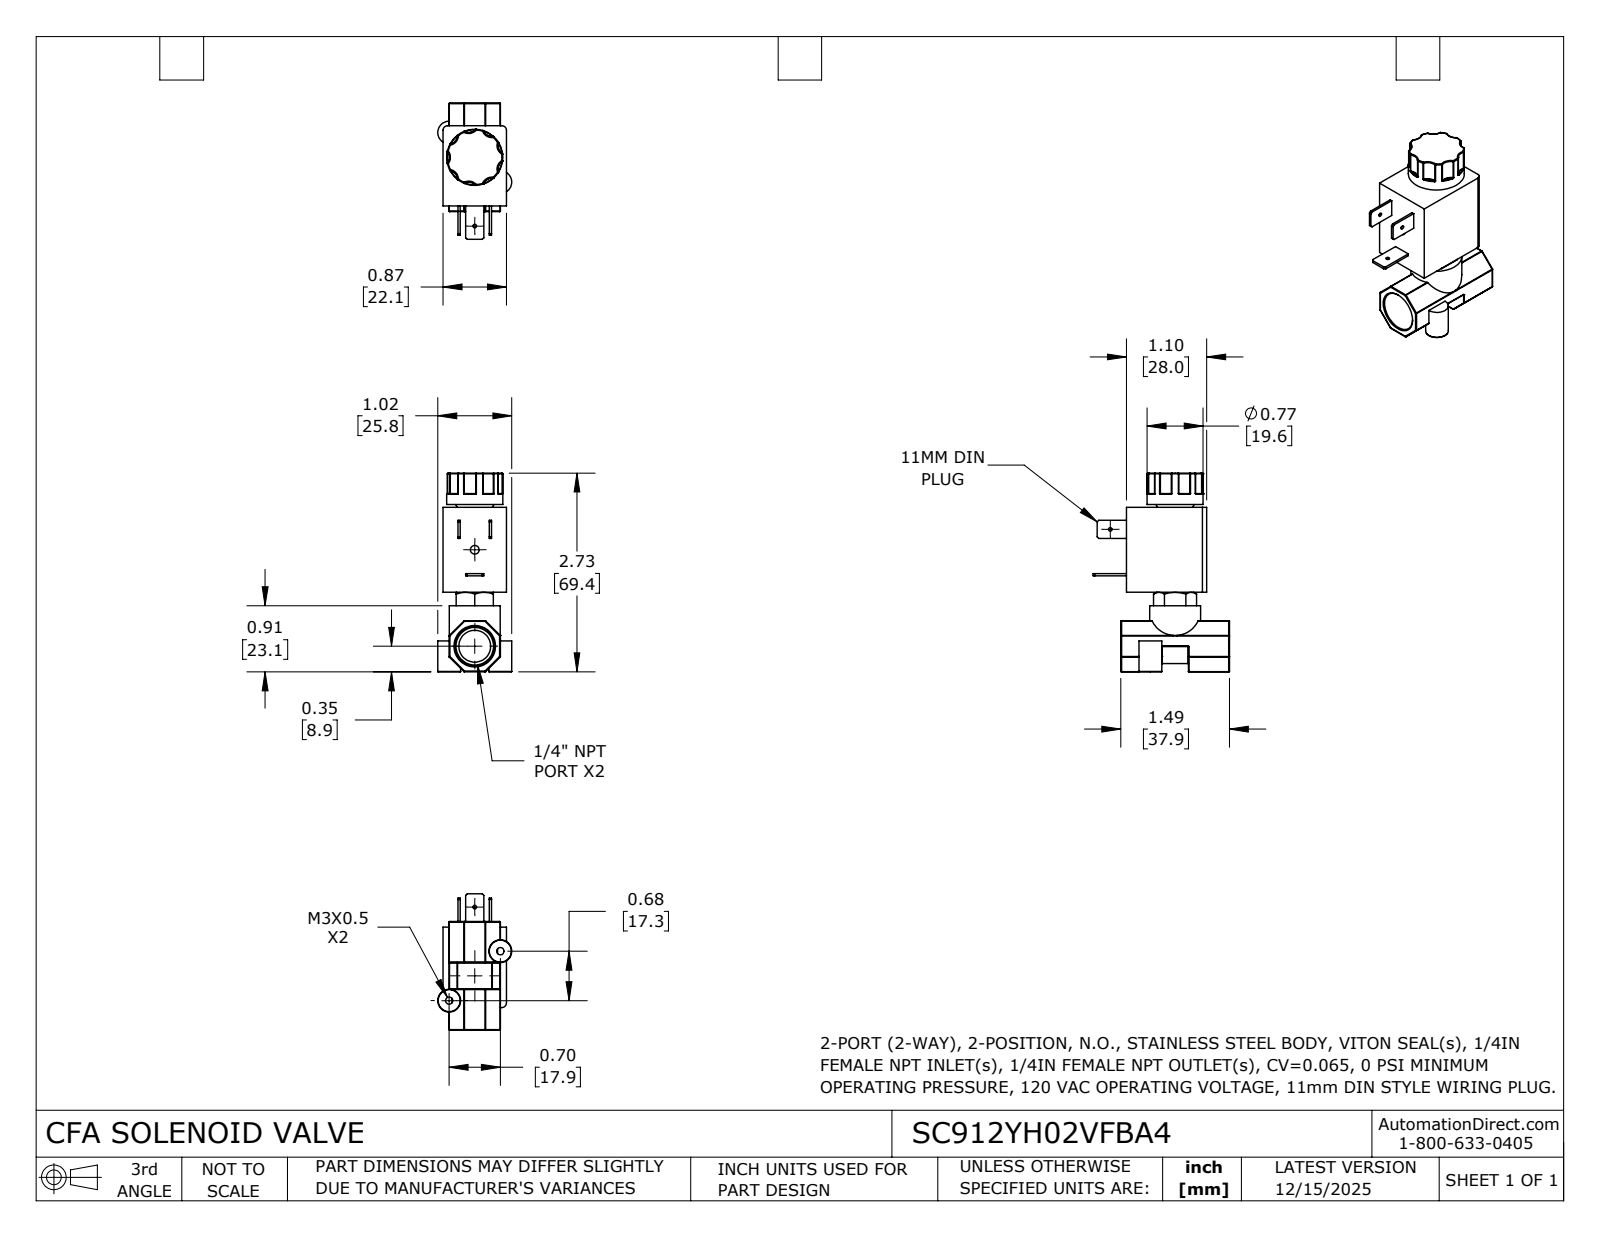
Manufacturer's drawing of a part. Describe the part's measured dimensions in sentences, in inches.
The part is named "SC912YH02VFBA4". Its 3-D file was written by "SolidWorks 2024 (CONFIG_CONTROL_DESIGN)". It is 1 solid with 350 faces: 74 planar, 107 cylindrical and 169 other. Overall it measures 2.731 by 1.874 by 1.017 inches. Its volume is 1.823 cubic inches and its surface area 16.29 square inches. Round holes: 2 of diameter 0.05, 2 of diameter 0.1, 1 of diameter 0.12, 1 of diameter 0.438. Round bosses or shafts: 2 of diameter 0.313, 1 of diameter 0.77, 1 of diameter 0.7. Partial cylindrical surfaces (rounded edges, fillets, slot ends): 42 of radius 0.01, 14 of radius 0.005, 7 of radius 0.133, 2 of radius 0.06, 2 of radius 0.132, 1 of radius 0.237, 1 of radius 0.314. The main face-to-face distances are 0.87, 0.704, 1.104, 1.167, 0.083, 0.787, 1.094, 2.261, 2.731, 1.637. The hole center spacings are 0.7, 0.979, 1.326, 1.333.
